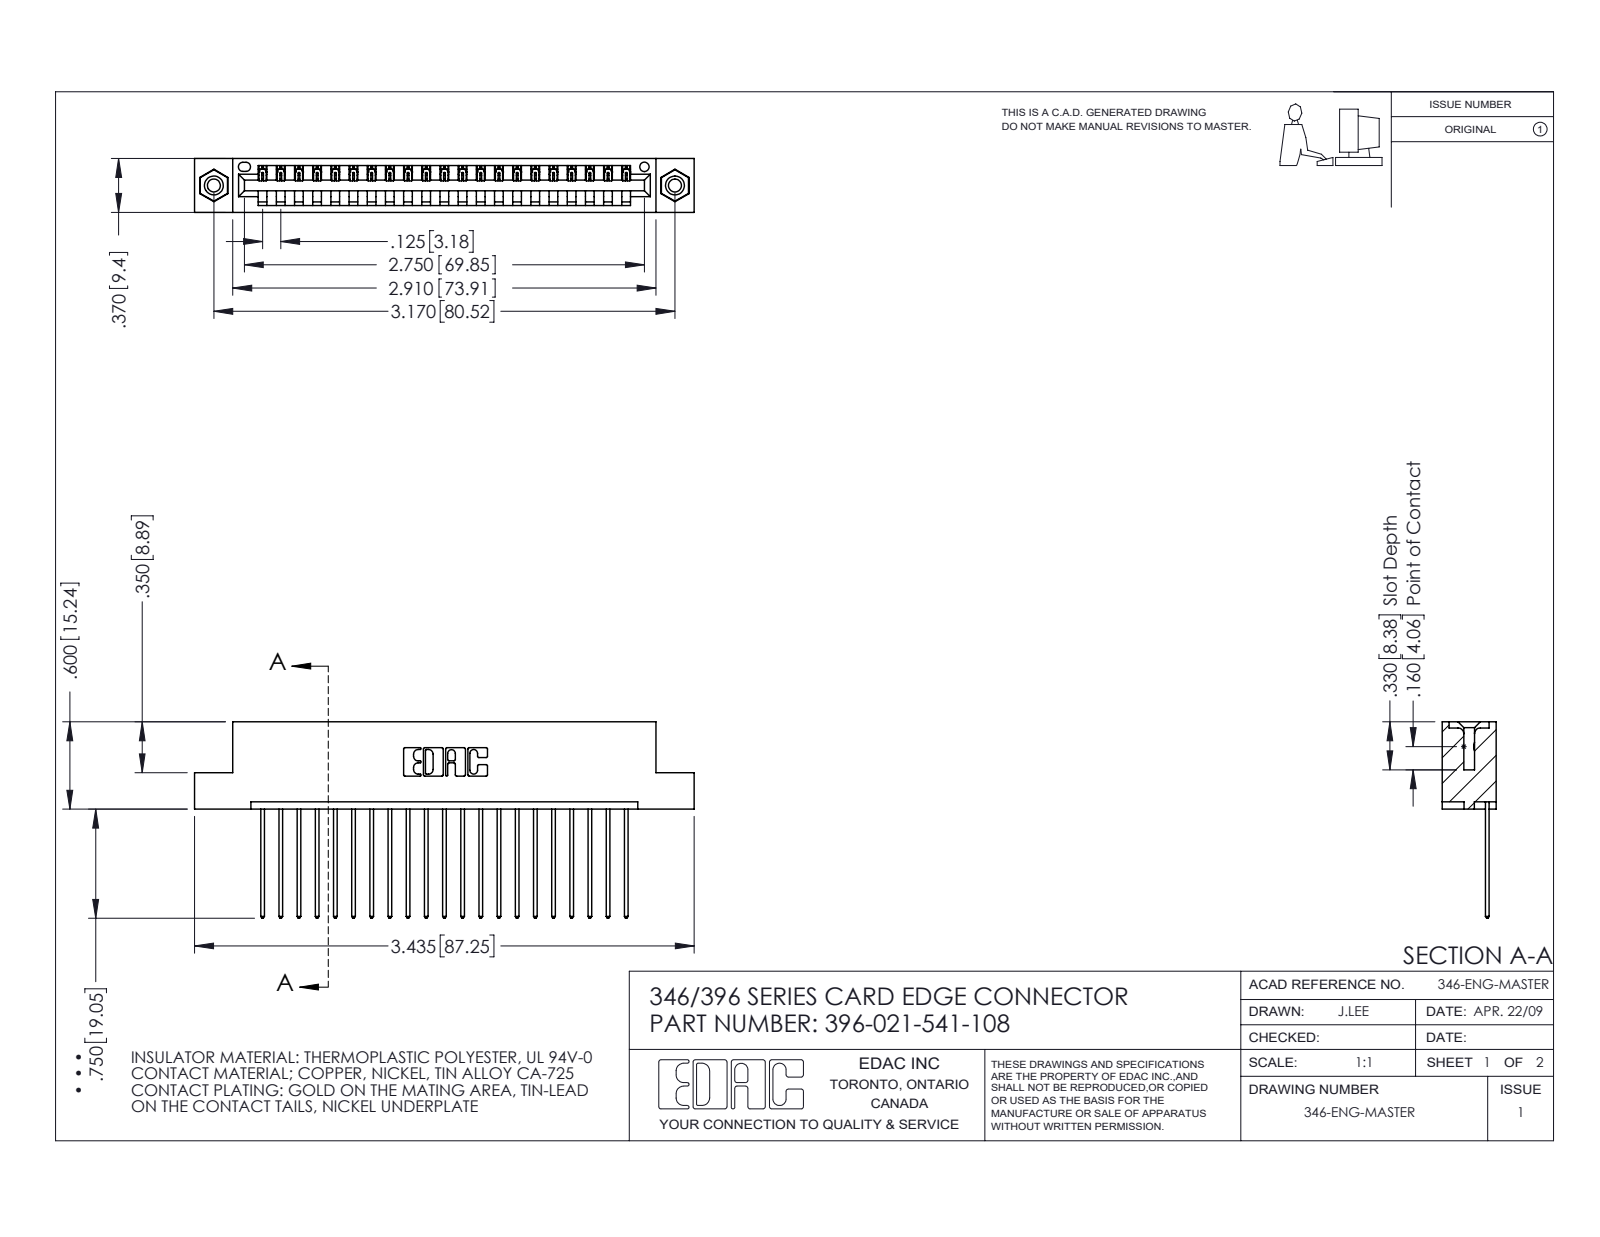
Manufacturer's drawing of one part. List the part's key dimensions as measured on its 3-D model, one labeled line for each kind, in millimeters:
Part name (STEP PRODUCT): 345-292-001_345-293-141; 396-021-541-108; 346 Part_Flush Mounting Lugs - 0.156 Dia-TI; 345-250-001_345-250-003-102
STEP written by: SolidWorks 2016 (CONFIG_CONTROL_DESIGN)
Units: millimetres
Bodies: 24 solids, 1400 faces (948 planar, 436 cylindrical, 16 other)
Overall size (bounding box): 87.2 × 34.3 × 9.4
Volume: 8 280 mm³ · Surface area: 10 550 mm²
Round holes (diameter × count): ⌀2.3 ×2, ⌀3.2 ×2, ⌀4 ×2, ⌀1.6 ×1
Round bosses / shafts (diameter × count): ⌀3.9 ×2
Partial cylindrical surfaces — rounded edges, fillets, slot ends (radius × count): R0.2 ×42, R0.3 ×42, R0.3 ×22, R0.2 ×6, R0.8 ×6, R0.7 ×3, R0.8 ×2, R1 ×2
Main face-to-face distances: 1.2, 8.2, 6.4, 9.4, 1.8, 7.6, 0.6, 3.8, 5.6, 2.5
Hole centre spacings: 6.2, 75.3, 80.5
